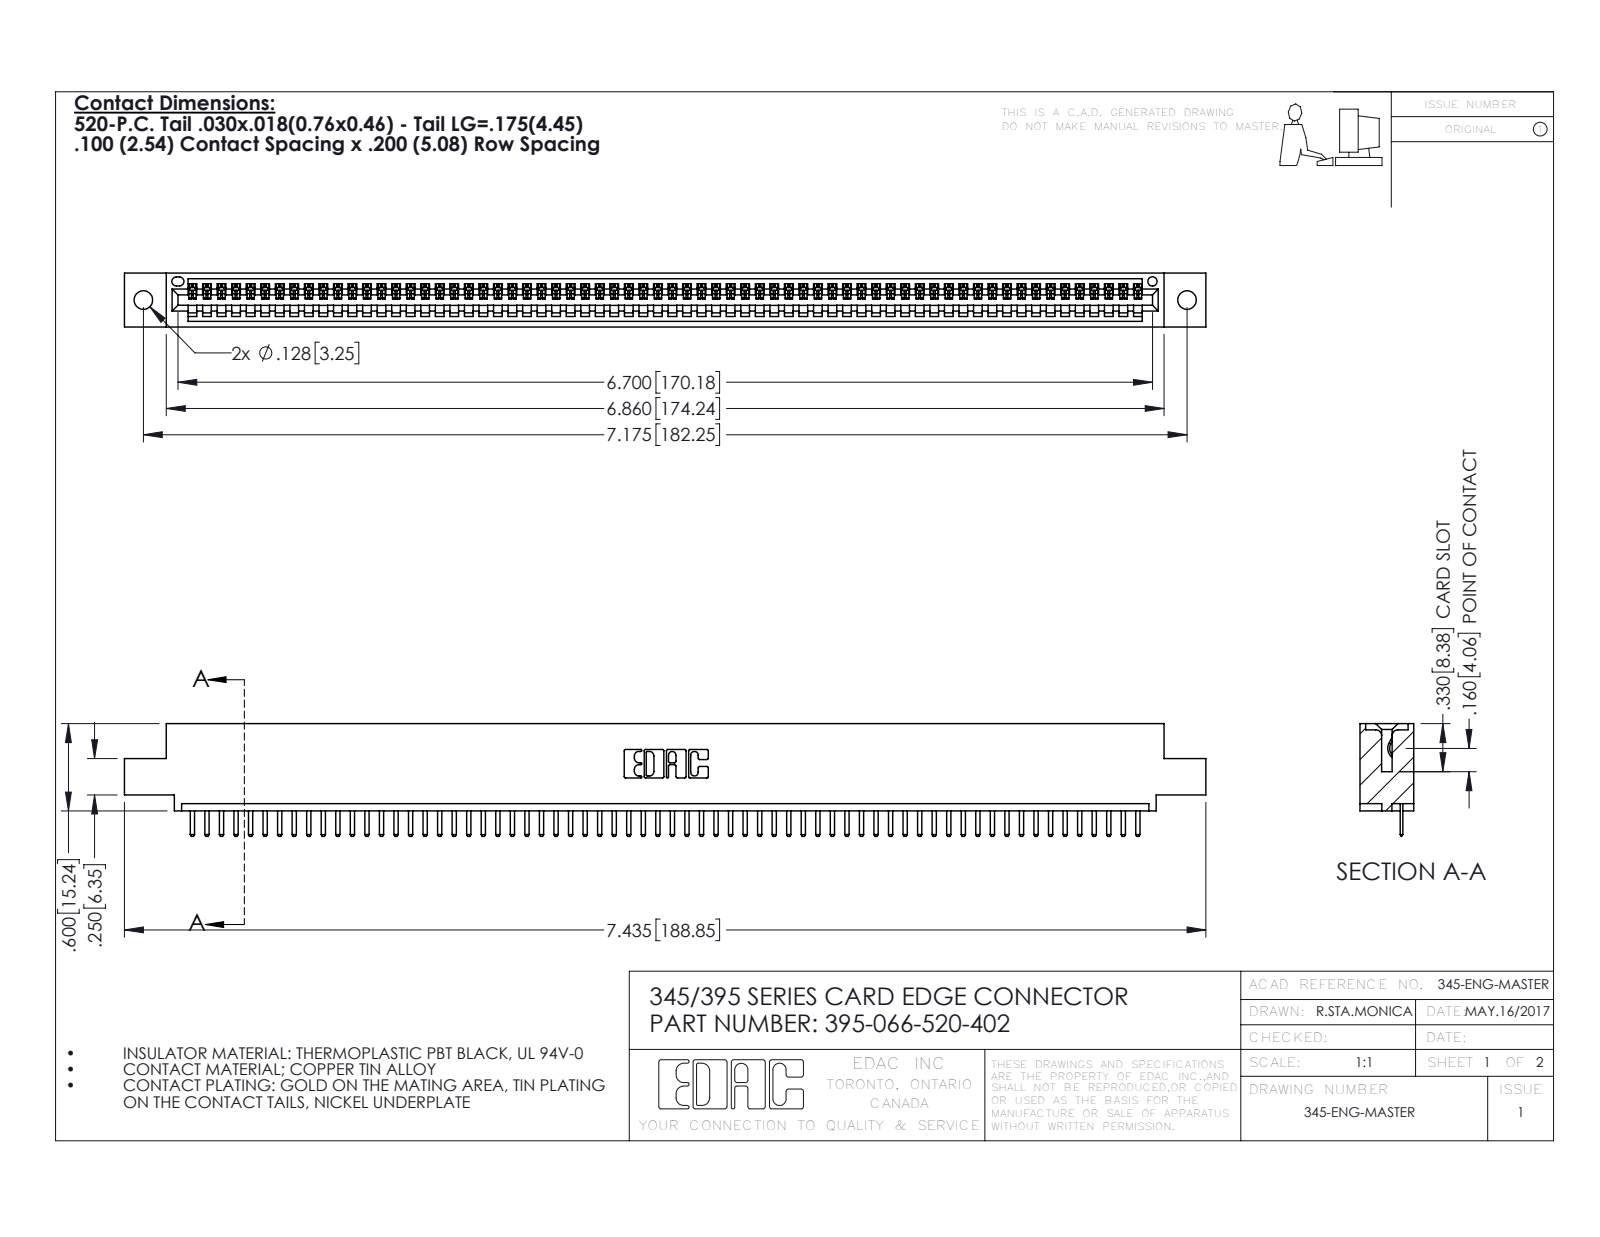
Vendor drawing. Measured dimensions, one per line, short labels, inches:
name: 395-066-520-402; 345 Part_0.110 Offset - 0.128 Dia; 345-292-001_345-293-120
written by: SolidWorks 2016 (CONFIG_CONTROL_DESIGN)
unit: in
bodies: 67 solids, 4222 faces (2856 planar, 1366 cylindrical, 0 other)
size: 7.435 × 0.775 × 0.37
volume: 1.088 in³; area: 35.98 in²
holes: 2× ⌀0.128, 1× ⌀0.064
rounds: 134× R0.01, 132× R0.006, 22× R0.01, 6× R0.007, 6× R0.031, 3× R0.026, 2× R0.031, 2× R0.04
face distances: 0.298, 0.072, 0.37, 0.2, 0.098, 0.272, 0.025, 0.225, 0.072, 0.149
hole spacings: 0.27, 6.939, 7.175
